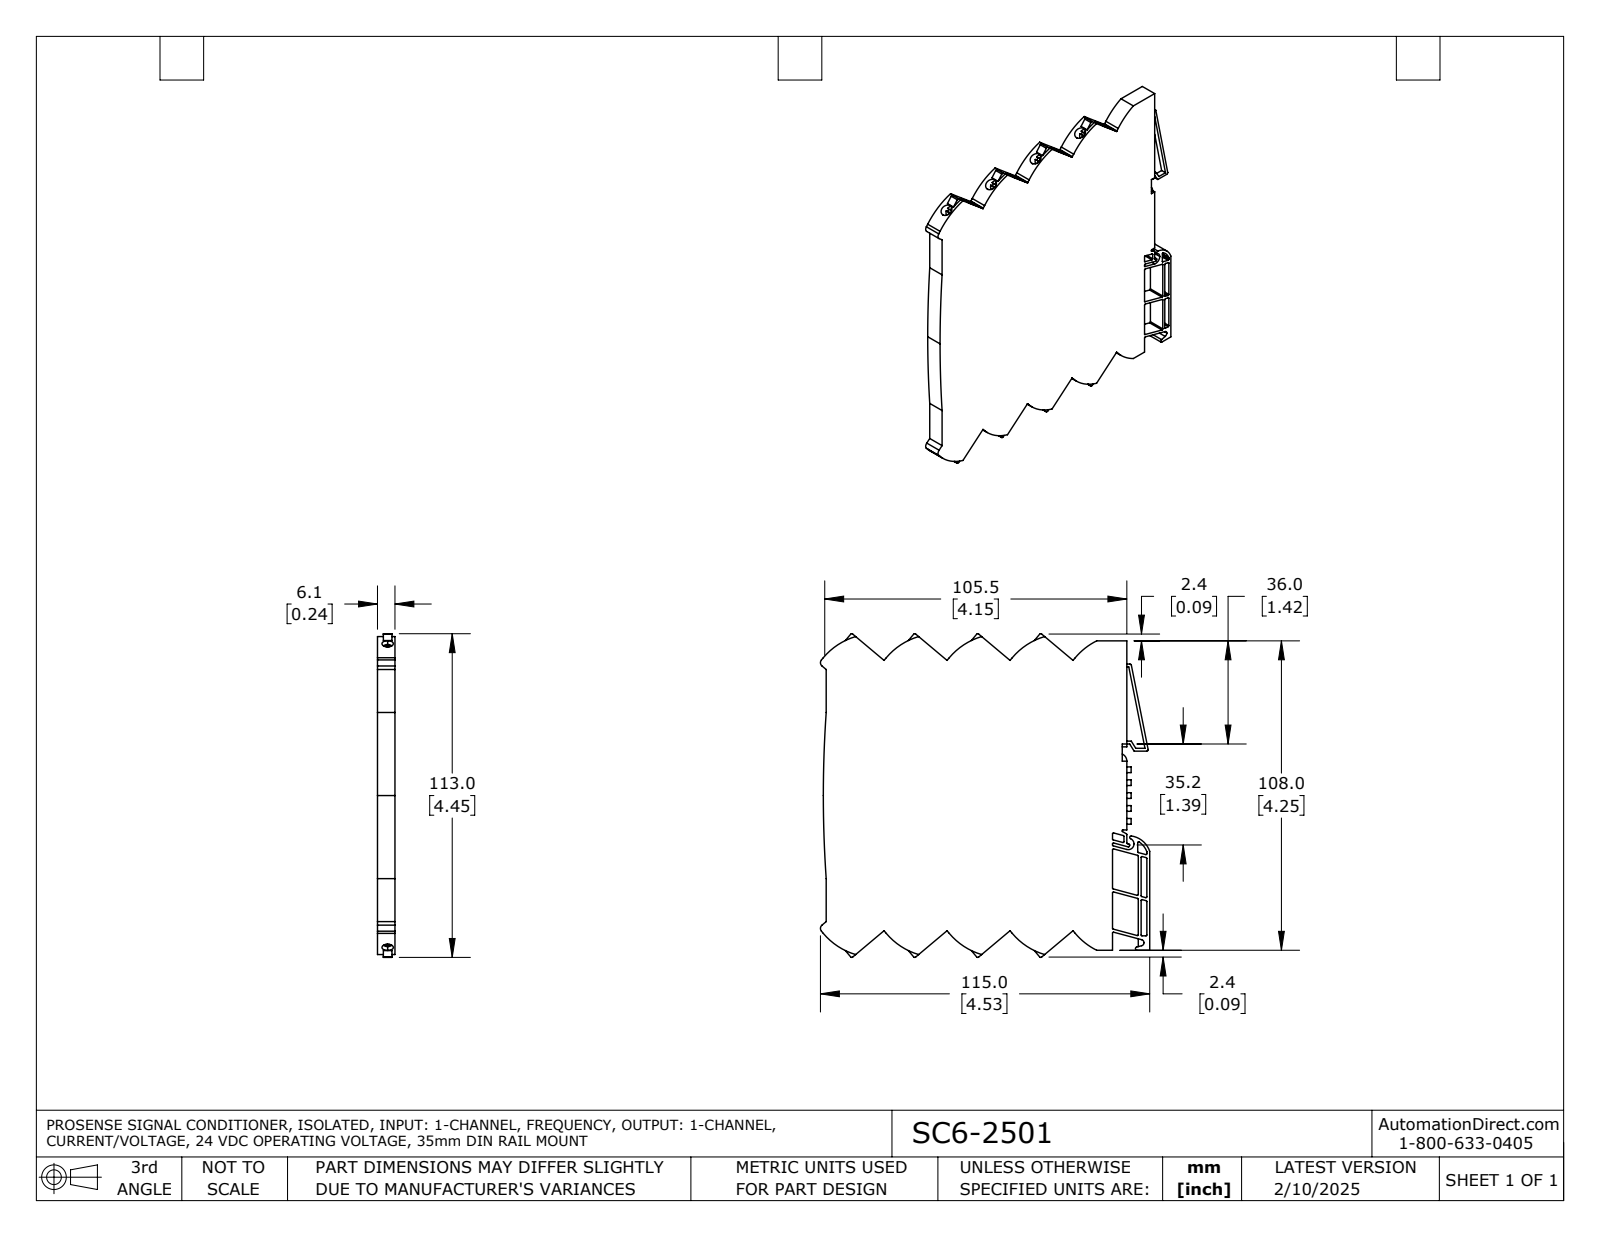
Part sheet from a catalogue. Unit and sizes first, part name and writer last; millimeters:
Units: millimetres
Overall size (bounding box): 115 × 113 × 6.1
Round holes (diameter × count): ⌀4 ×8
Partial cylindrical surfaces — rounded edges, fillets, slot ends (radius × count): R0.3 ×32, R0.5 ×11, R1.5 ×10, R23.3 ×10, R0.6 ×1, R1.1 ×1, R1.5 ×1, R1.8 ×1
Main face-to-face distances: 6.1, 1, 3, 4, 2.1, 14.1, 4, 16.8, 1, 2
Hole centre spacings: 14.1, 28.3, 14.1, 42.4
Volume: 65 480 mm³ · Surface area: 28 500 mm²
Bodies: 1 solid, 457 faces (333 planar, 124 cylindrical, 0 other)
Part name (STEP PRODUCT): SC6-2501
STEP written by: SolidWorks 2021 (AUTOMOTIVE_DESIGN)
